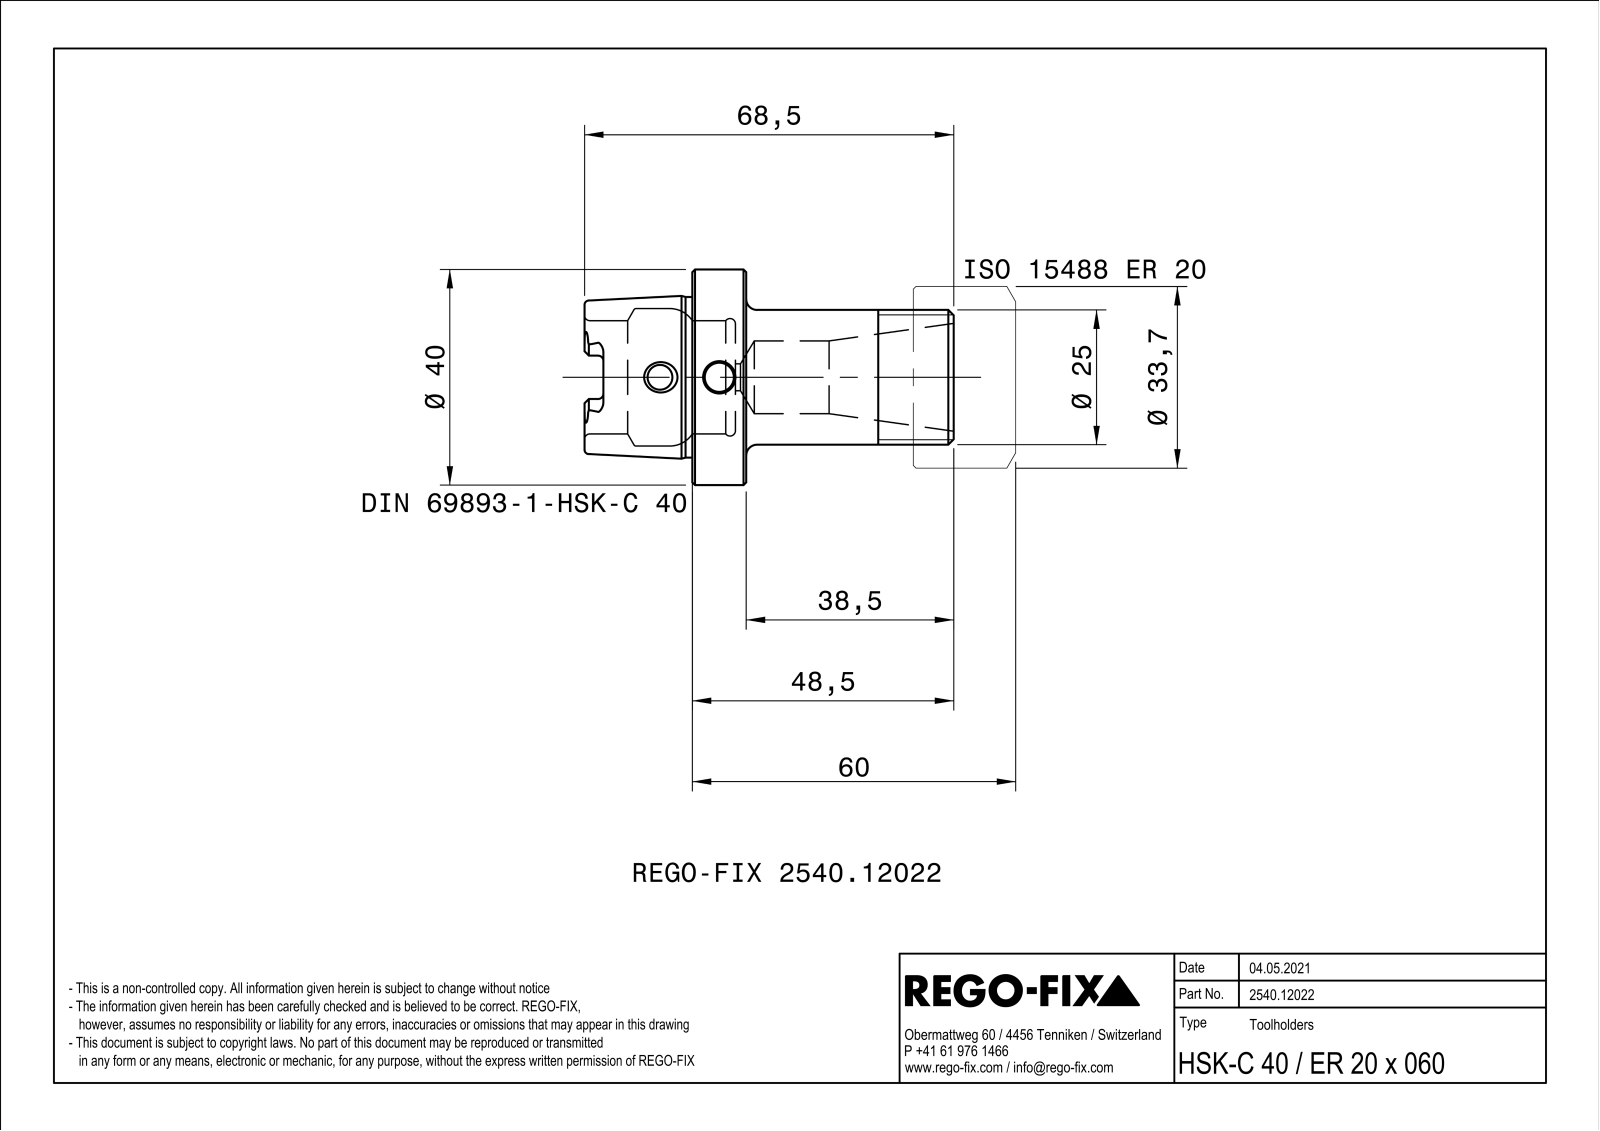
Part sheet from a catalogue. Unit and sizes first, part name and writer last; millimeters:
Units: millimetres
Overall size (bounding box): 68.5 × 40 × 40
Round holes (diameter × count): ⌀4.6 ×1, ⌀5 ×1, ⌀6 ×1, ⌀13.5 ×1, ⌀21 ×1, ⌀25.5 ×1
Round bosses / shafts (diameter × count): ⌀40 ×1, ⌀29.91 ×1, ⌀25 ×1
Partial cylindrical surfaces — rounded edges, fillets, slot ends (radius × count): R1 ×6, R1.88 ×4
Main face-to-face distances: 10, 2, 8, 30, 28, 20, 38.5, 40.5, 48.5, 68.5
Hole centre spacings: 11
Volume: 25 815 mm³ · Surface area: 12 004 mm²
Bodies: 1 solid, 78 faces (23 planar, 22 cylindrical, 33 other)
Part name (STEP PRODUCT): NOCUT
STEP written by: SIEMENS PLM Software Solid Edge ST10 (AUTOMOTIVE_DESIGN)
